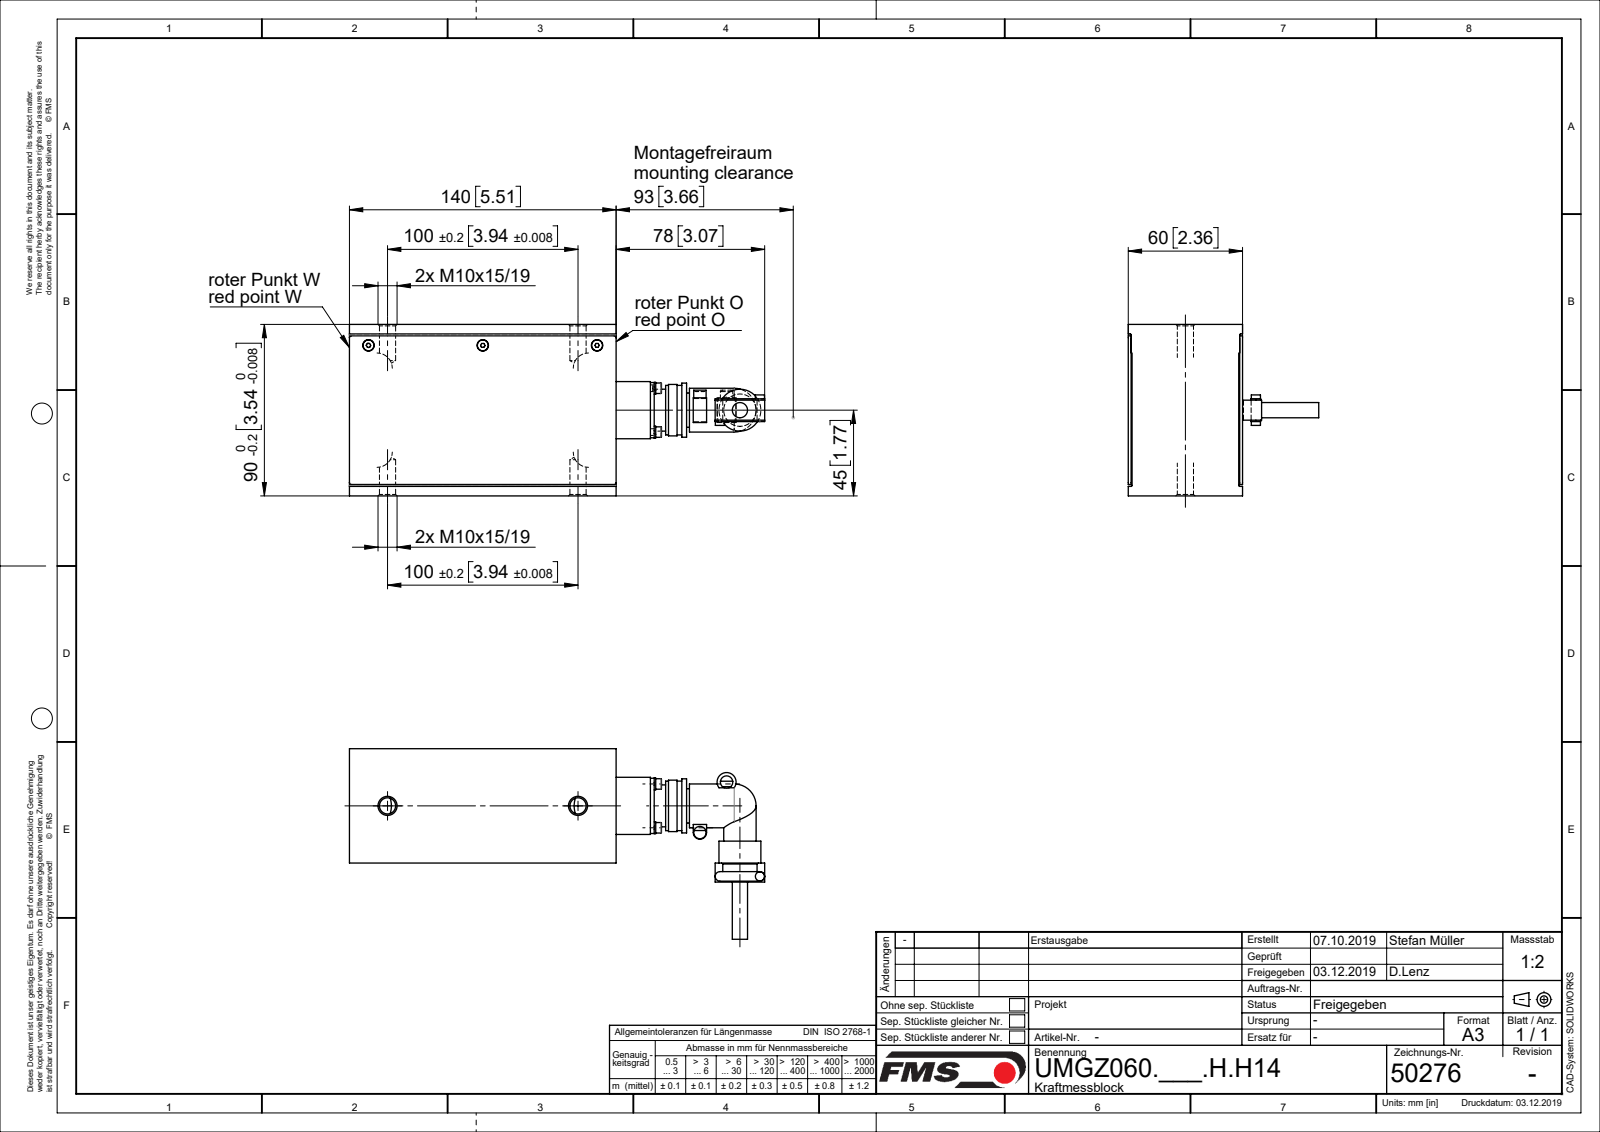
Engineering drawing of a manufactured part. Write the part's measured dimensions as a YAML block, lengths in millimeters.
part_name: "U50276; U4945304; U49515; SENKSCHRAUBE_I-6KT_M3X6 (+6 more)"
step_written_by: "Mechanical Desktop 2007 (CONFIG_CONTROL_DESIGN)"
units: millimeters
bodies: {solids: 19, faces: 399, planar: 156, cylindrical: 160, other: 83}
overall_size: [218, 100, 90]
volume: 780414
surface_area: 119811
round_holes:
  - {diameter: 2.6, count: 7}
  - {diameter: 3.2, count: 4}
  - {diameter: 3.4, count: 4}
  - {diameter: 3.5, count: 4}
  - {diameter: 6, count: 3}
  - {diameter: 8.68, count: 2}
  - {diameter: 23, count: 1}
round_bosses_or_shafts:
  - {diameter: 3, count: 7}
  - {diameter: 6.2, count: 4}
  - {diameter: 5.5, count: 4}
  - {diameter: 22, count: 2}
  - {diameter: 6.5, count: 2}
  - {diameter: 4.8, count: 2}
  - {diameter: 28.4, count: 1}
  - {diameter: 27, count: 1}
partial_cylinders:
  - {radius: 1, count: 4}
  - {radius: 2.5, count: 2}
  - {radius: 3.5, count: 1}
  - {radius: 5, count: 1}
face_to_face_distances: [1.5, 58.5, 2, 0.5, 58, 56.5, 60, 57, 56, 90]
hole_center_spacings: [16.26, 23, 32.53, 60, 100, 120]
